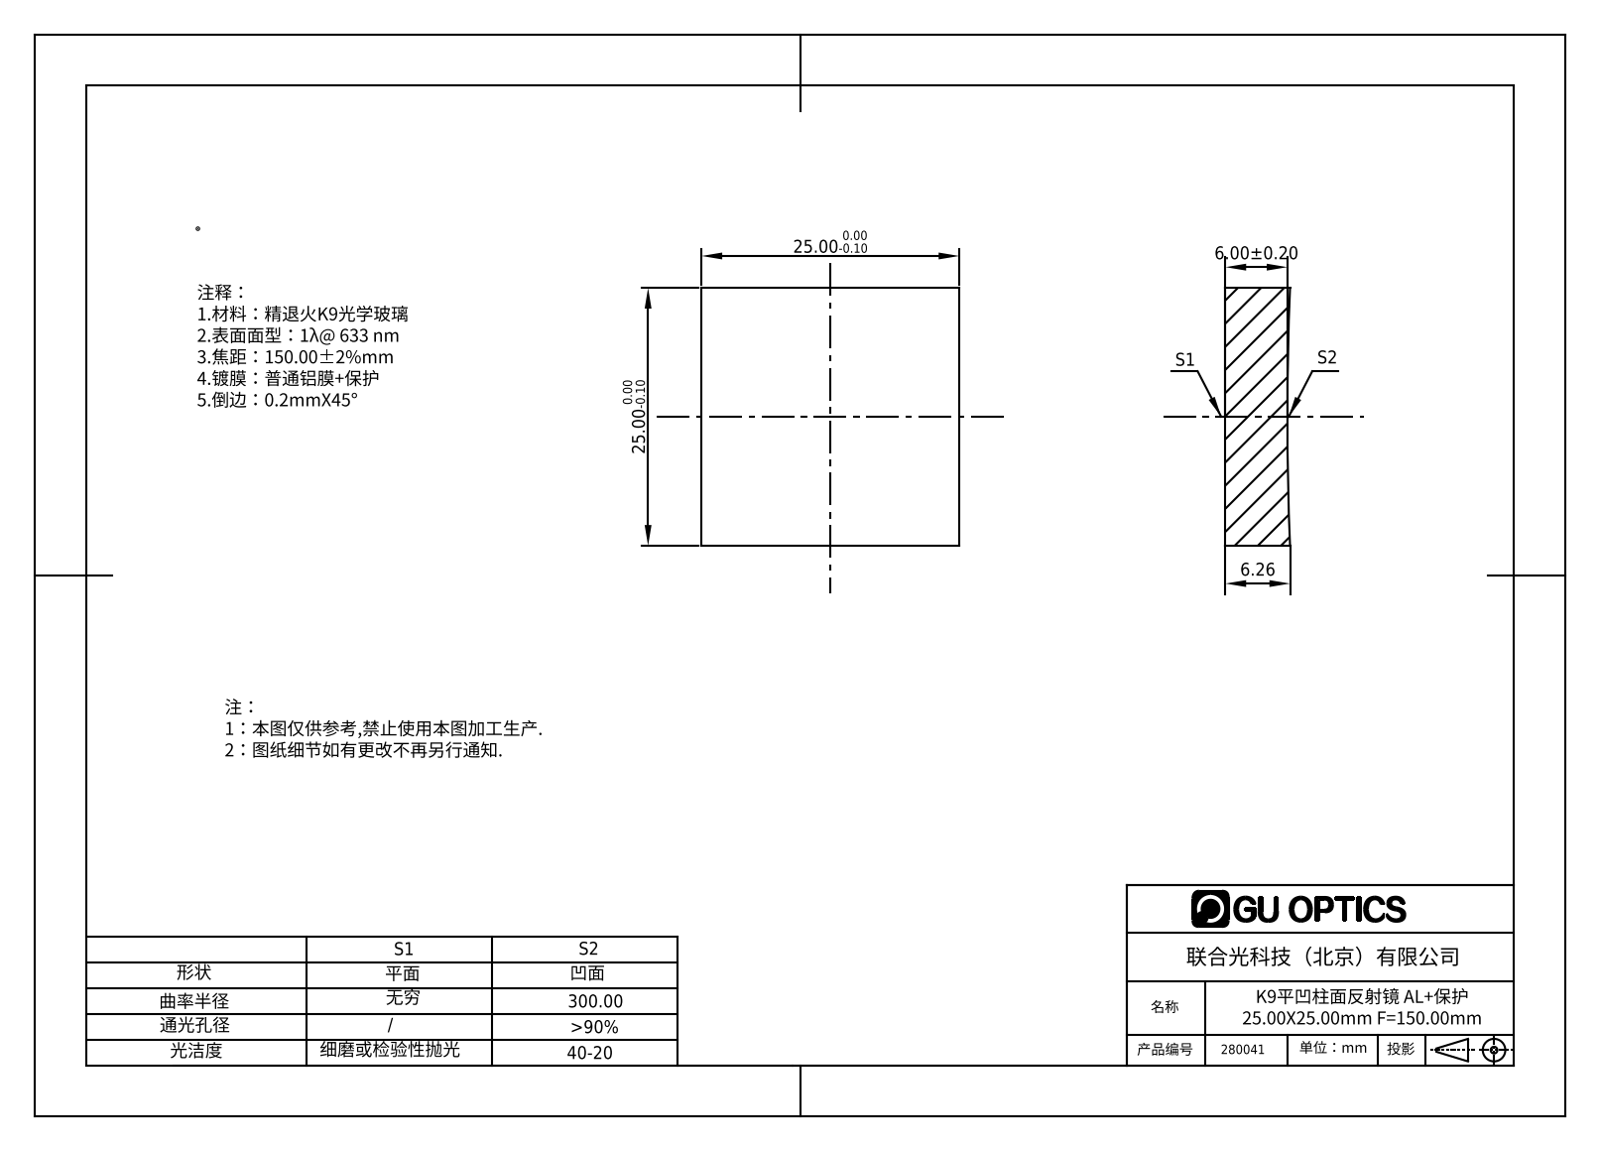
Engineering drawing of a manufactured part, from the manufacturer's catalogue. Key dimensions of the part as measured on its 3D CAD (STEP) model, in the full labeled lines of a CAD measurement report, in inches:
Part name (STEP PRODUCT): 280019
STEP written by: SolidWorks 2016 (AUTOMOTIVE_DESIGN)
Units: inches
Bodies: 1 solid, 7 faces (5 planar, 2 cylindrical, 0 other)
Overall size (bounding box): 0.984 × 0.984 × 0.246
Volume: 0.232 in³ · Surface area: 2.895 in²
Partial cylindrical surfaces — rounded edges, fillets, slot ends (radius × count): R11.811 ×1
Main face-to-face distances: 0.984
